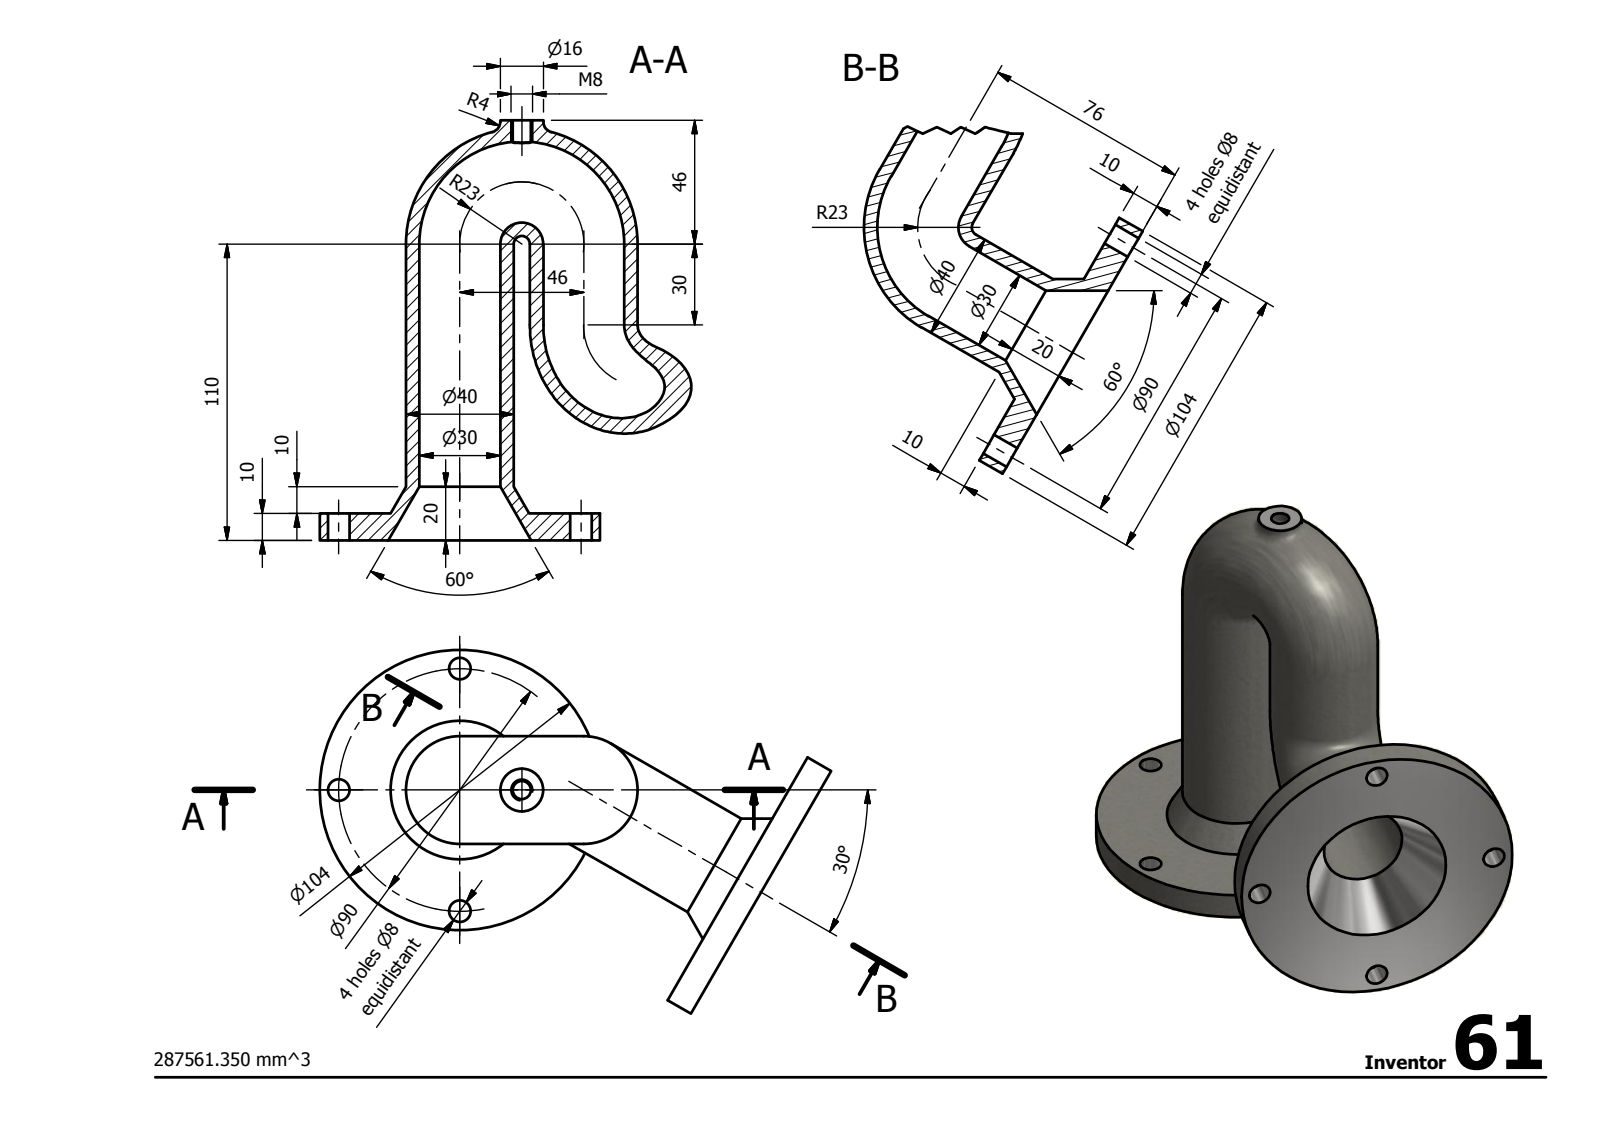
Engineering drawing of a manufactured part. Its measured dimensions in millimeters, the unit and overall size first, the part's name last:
Units: millimetres
Overall size (bounding box): 189.82 × 156 × 135.03
Round holes (diameter × count): ⌀8 ×8, ⌀30 ×3, ⌀6.65 ×1
Round bosses / shafts (diameter × count): ⌀40 ×3, ⌀104 ×2, ⌀16 ×1
Main face-to-face distances: 10, 156, 146
Hole centre spacings: 45, 63.64, 90, 23, 50.54, 64.35, 1, 22
Volume: 287 559 mm³ · Surface area: 100 227 mm²
Bodies: 1 solid, 32 faces (5 planar, 18 cylindrical, 9 other)
STEP written by: Autodesk Inventor 2014 (AUTOMOTIVE_DESIGN)
